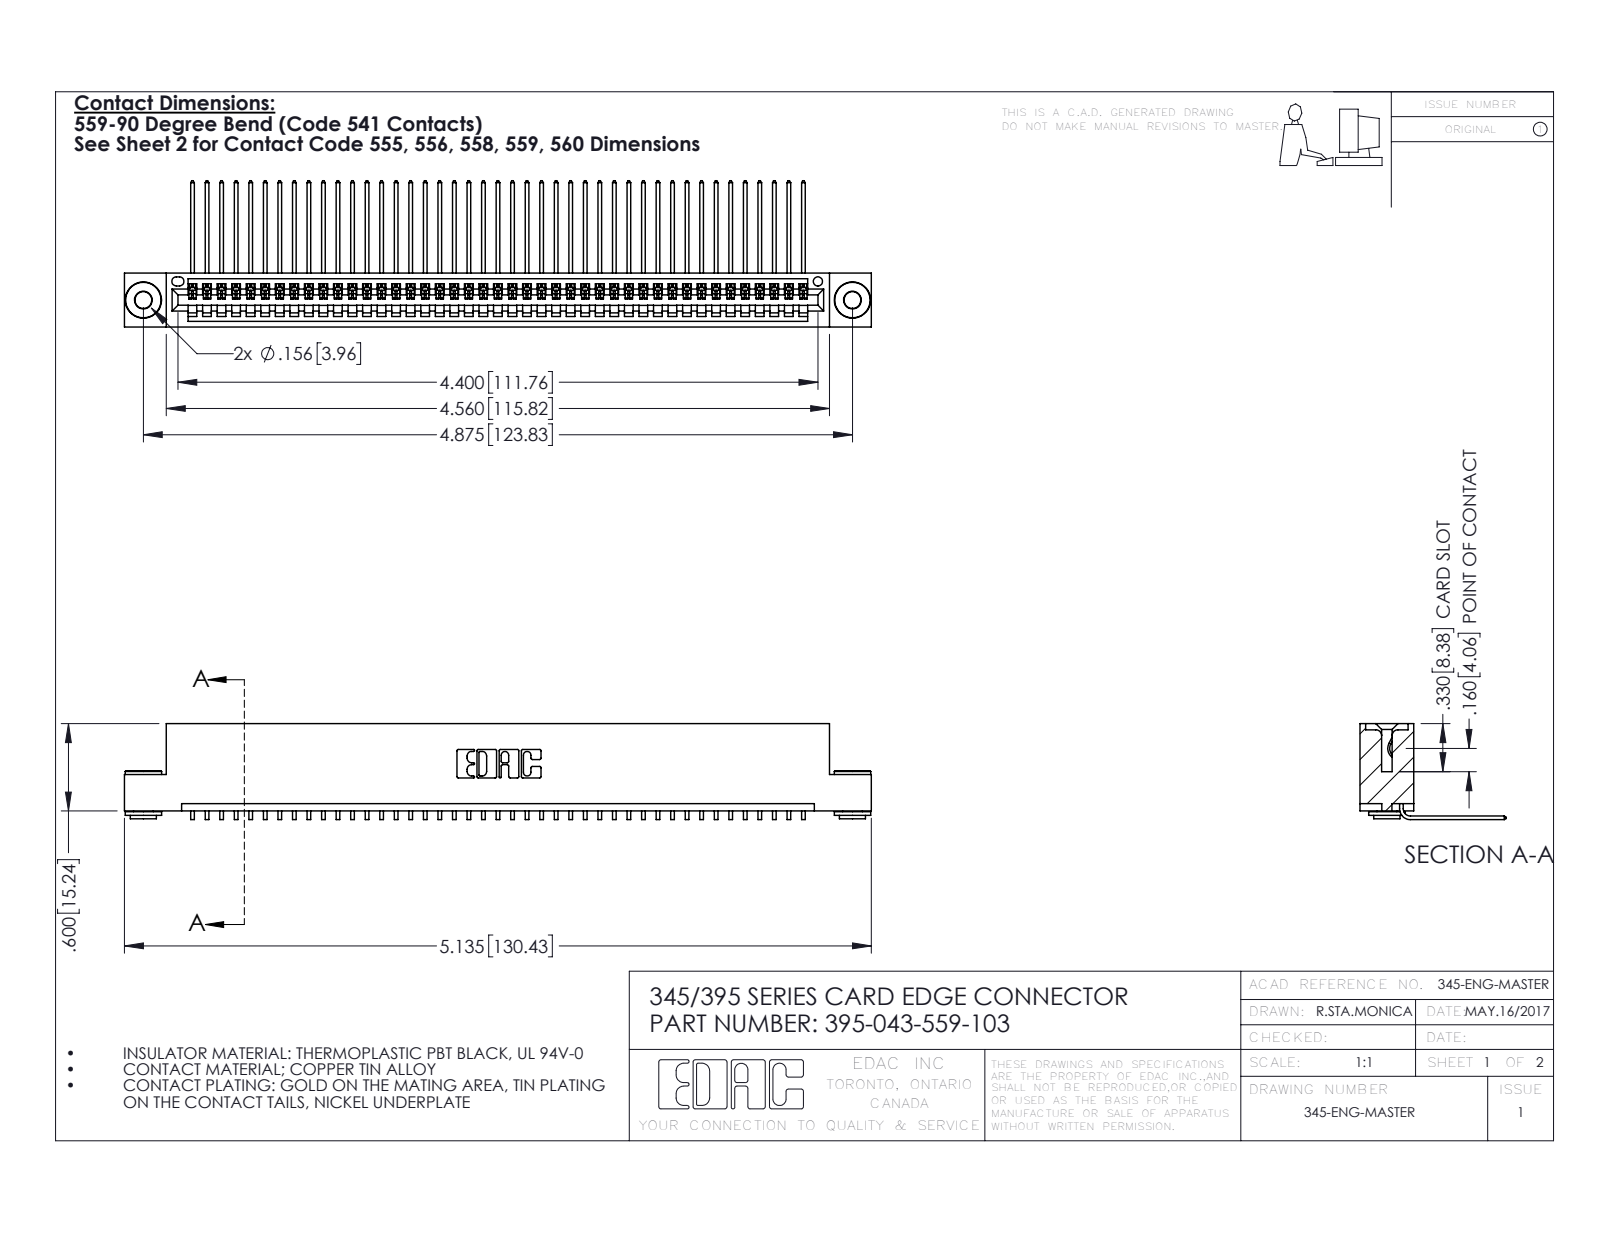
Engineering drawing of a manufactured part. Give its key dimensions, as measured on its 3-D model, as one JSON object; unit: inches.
{"part_name": "345-250-002_345-250-002-102; 395-043-559-103; 345-292-001_558 559 Tail - 1; 345 Part_Flush Mounting Lugs - 0.156 Dia-TH", "step_written_by": "SolidWorks 2016 (CONFIG_CONTROL_DESIGN)", "units": "inches", "bodies": {"solids": 46, "faces": 2744, "planar": 1896, "cylindrical": 840, "other": 8}, "overall_size": [5.135, 1.005, 0.659], "volume_in3": 0.766, "surface_area_in2": 27.53, "round_holes": [[0.116, 2], [0.156, 2], [0.064, 1]], "round_bosses_or_shafts": [[0.25, 2], [0.18, 2], [0.136, 2]], "partial_cylinders_radius": [[0.006, 86], [0.01, 22], [0.007, 6], [0.031, 6], [0.026, 3], [0.031, 2], [0.04, 2], [0.014, 1]], "face_to_face_distances": [0.072, 0.298, 0.37, 0.2, 0.025, 0.098, 0.272, 0.225, 0.149, 0.072], "hole_center_spacings": [0.27, 4.639, 4.875]}
